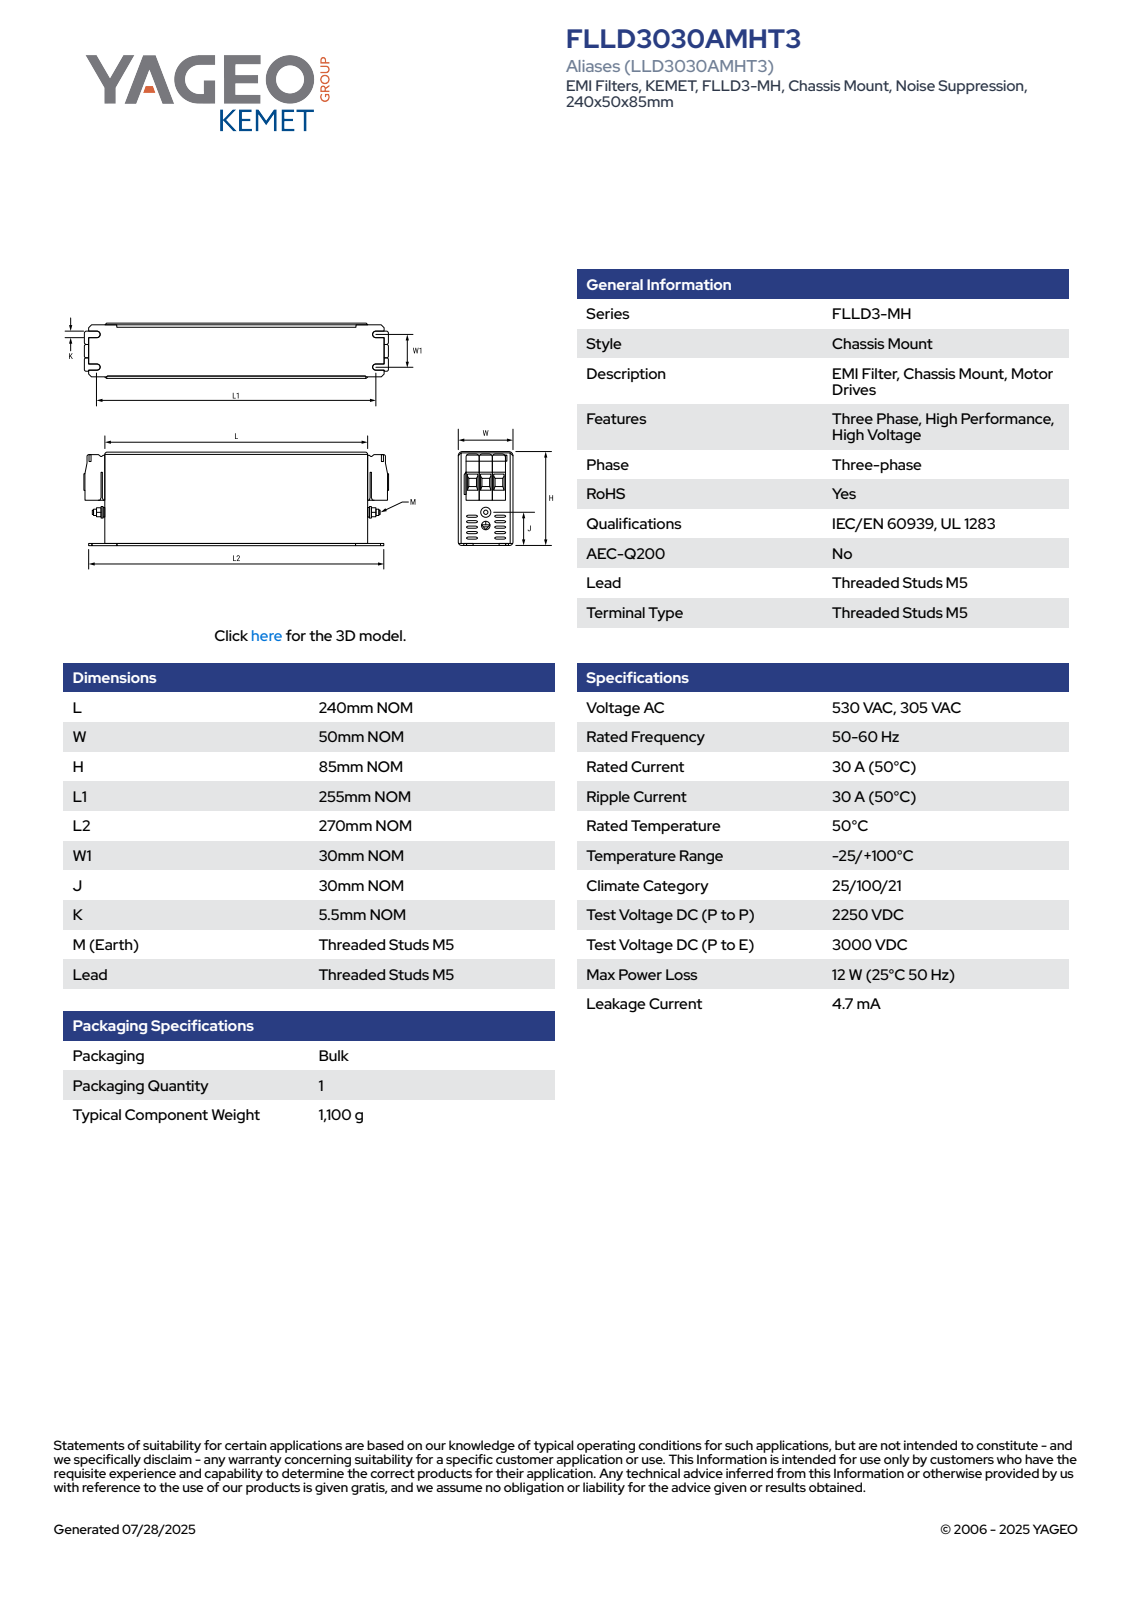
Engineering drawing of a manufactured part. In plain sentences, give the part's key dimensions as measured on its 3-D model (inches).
The part is named "EFC_KFLLD3MH_L240W50H85L1255L2270W130". Its 3-D file was written by "SolidWorks 2014 (AUTOMOTIVE_DESIGN)". It is 4 solids with 153 faces: 117 planar, 32 cylindrical and 4 other. Overall it measures 10.63 by 3.346 by 1.969 inches. Its volume is 62.85 cubic inches and its surface area 122.5 square inches. Round bosses or shafts: 1 of diameter 0.315, 1 of diameter 0.236, 1 of diameter 0.197. Partial cylindrical surfaces (rounded edges, fillets, slot ends): 8 of radius 0.157, 4 of radius 0.079, 4 of radius 0.108. The main face-to-face distances are 1.969, 3.346, 9.449, 0.039, 0.433, 9.764, 0.315, 3.307, 0.394, 0.354.
